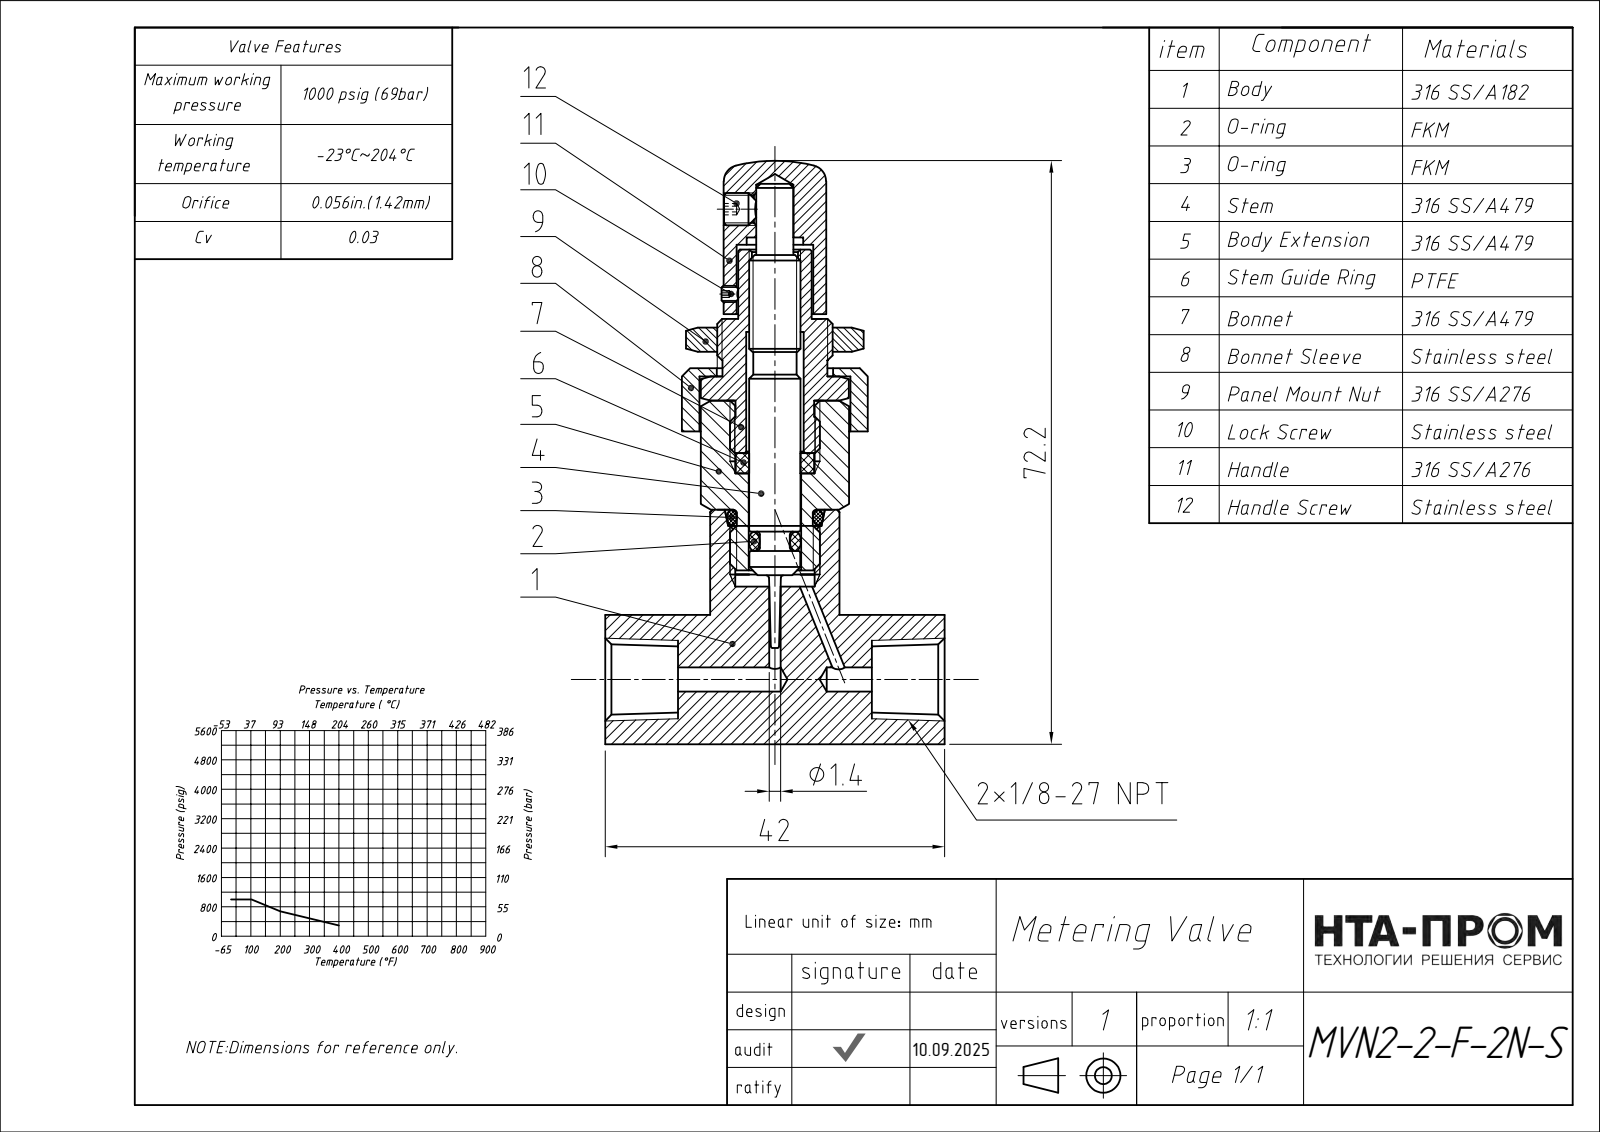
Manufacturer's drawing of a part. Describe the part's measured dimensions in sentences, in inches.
The part is named "MVN2-2-F-2N-S". Its 3-D file was written by "FreeCAD (AUTOMOTIVE_DESIGN)". It is 3 solids with 205 faces: 48 planar, 55 cylindrical and 102 other. Overall it measures 2.921 by 1.654 by 0.784 inches. Its volume is 1.157 cubic inches and its surface area 15.29 square inches. Round holes: 2 of diameter 0.055, 1 of diameter 0.118, 1 of diameter 0.224, 1 of diameter 0.256, 1 of diameter 0.276, 1 of diameter 0.374, 1 of diameter 0.387, 1 of diameter 0.438, 1 of diameter 0.567, 1 of diameter 0.736. Round bosses or shafts: 2 of diameter 0.63, 1 of diameter 0.722, 1 of diameter 0.722, 1 of diameter 0.562, 1 of diameter 0.511, 1 of diameter 0.5, 1 of diameter 0.37, 1 of diameter 0.358. Partial cylindrical surfaces (rounded edges, fillets, slot ends): 1 of radius 0.394. The main face-to-face distances are 0.784, 0.63, 0.077, 0.707, 0.118, 0.081, 0.199, 0.017, 0.767, 1.654.
